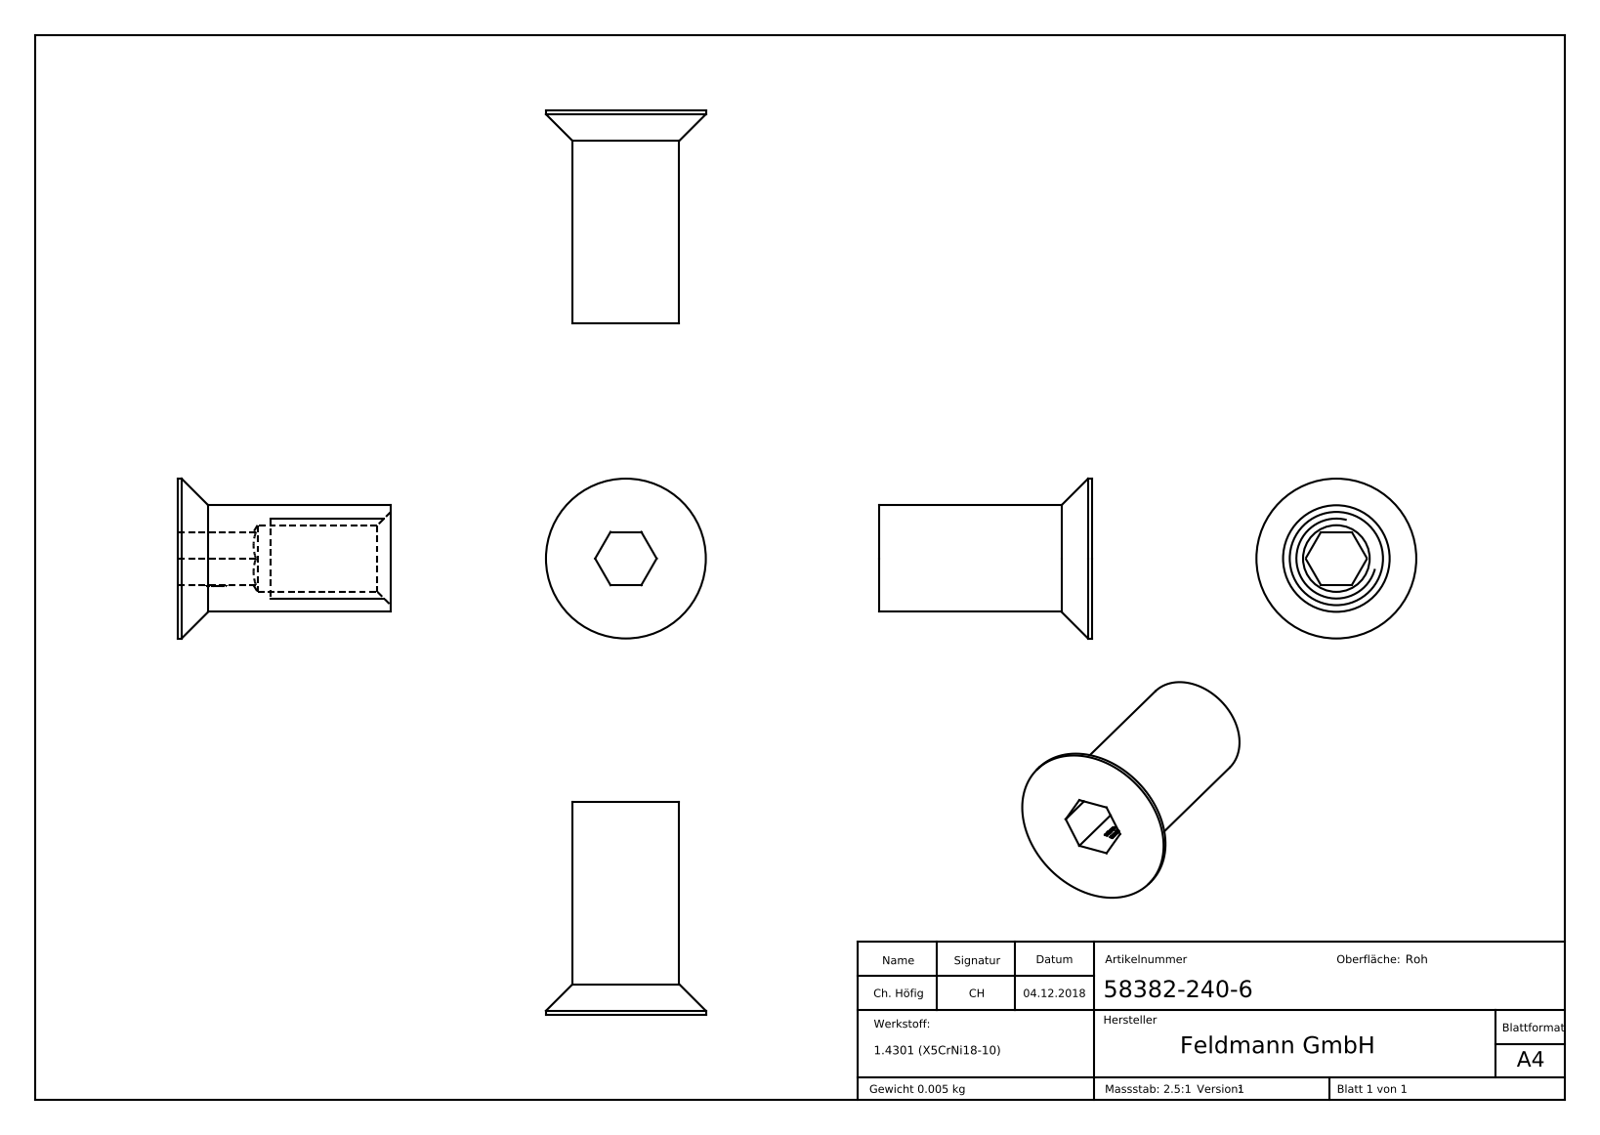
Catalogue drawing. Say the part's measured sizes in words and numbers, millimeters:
The part is named "58382-240-6". Its 3-D file was written by "SolidWorks 2015 (CONFIG_CONTROL_DESIGN)". It is 1 solid with 282 faces: 136 planar, 6 cylindrical and 140 other. Overall it measures 16 by 12 by 12 millimeters. Its volume is 593 cubic millimeters and its surface area 812 square millimeters. Round holes: 1 of diameter 5. Round bosses or shafts: 1 of diameter 12, 1 of diameter 8. The main face-to-face distances are 4, 16, 4.1, 0.5, 0.45, 0.48, 0.68, 0.51, 0.66, 0.43.
